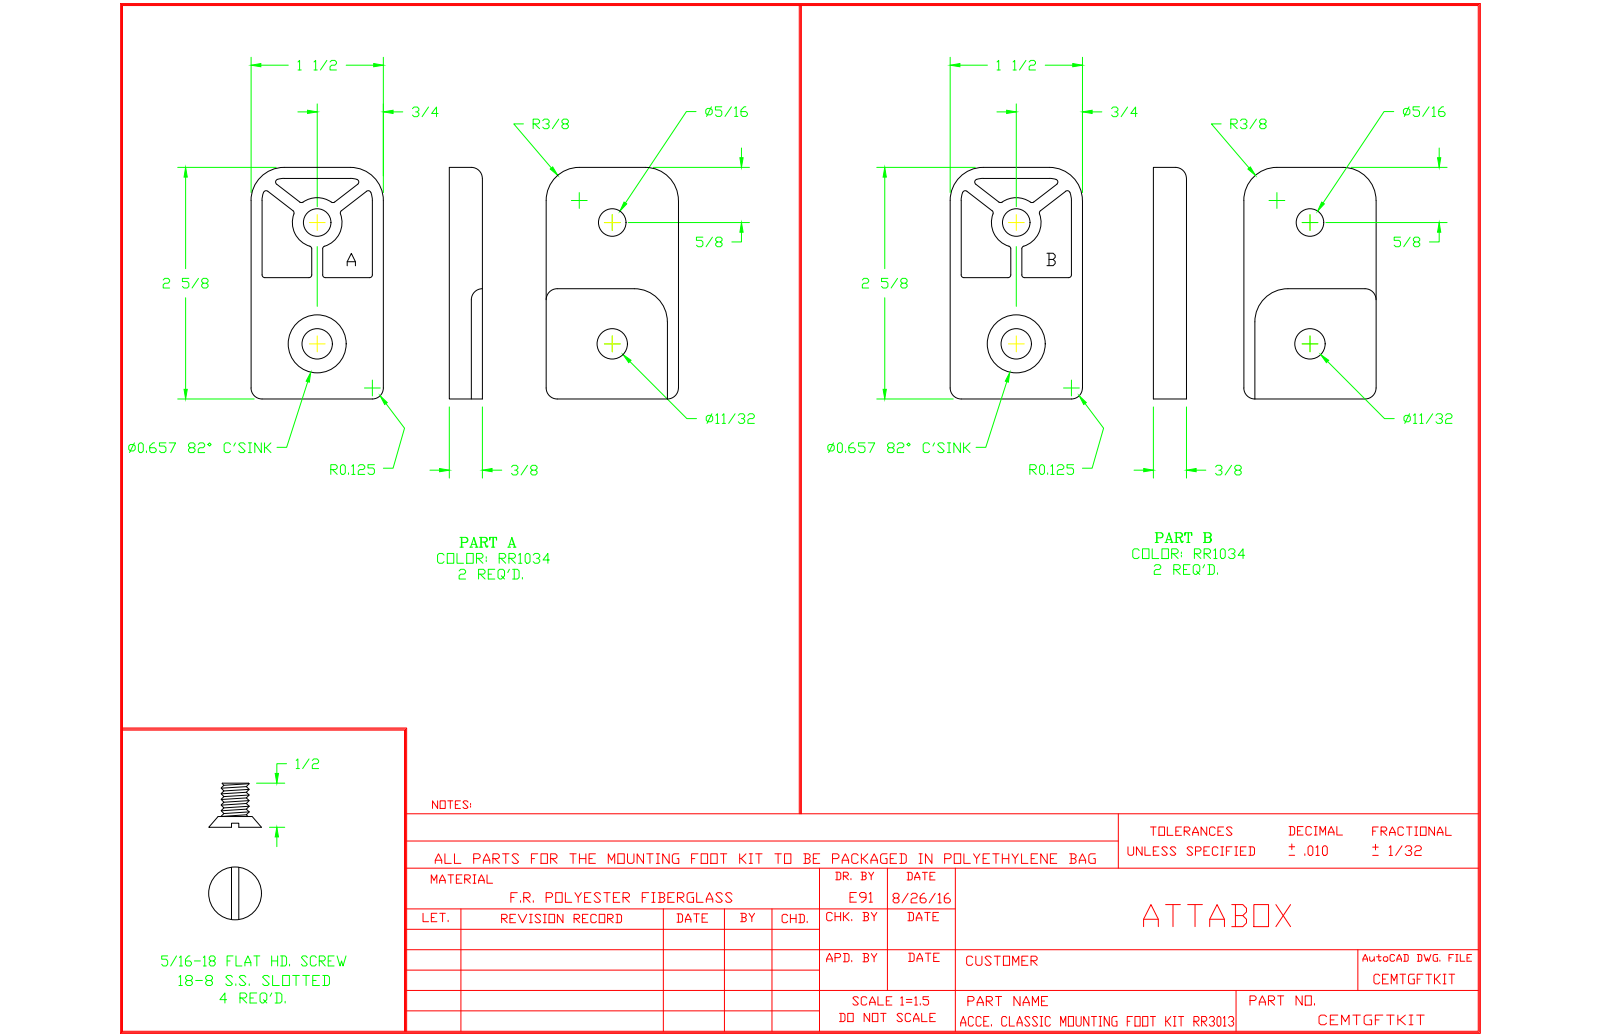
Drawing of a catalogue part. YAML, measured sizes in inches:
part_name: "CEMTGFTKIT"
step_written_by: "SolidWorks 2017 (AUTOMOTIVE_DESIGN)"
units: inches
bodies: {solids: 8, faces: 508, planar: 164, cylindrical: 176, other: 168}
overall_size: [6.237, 4.936, 0.787]
volume: 4.557
surface_area: 53.48
round_holes:
  - {diameter: 0.313, count: 4}
  - {diameter: 0.344, count: 4}
round_bosses_or_shafts:
  - {diameter: 0.622, count: 4}
  - {diameter: 0.315, count: 4}
partial_cylinders:
  - {radius: 0.031, count: 56}
  - {radius: 0.1, count: 12}
  - {radius: 0.25, count: 8}
  - {radius: 0.125, count: 4}
  - {radius: 0.281, count: 4}
  - {radius: 0.375, count: 2}
face_to_face_distances: [0.125, 0.25, 0.375, 0.125, 3.407, 0.402, 0.278, 0.152, 0.028, 3.578]
hole_center_spacings: [1.375, 1.375, 2.175, 3.384, 3.41, 3.55, 3.55, 3.665]
